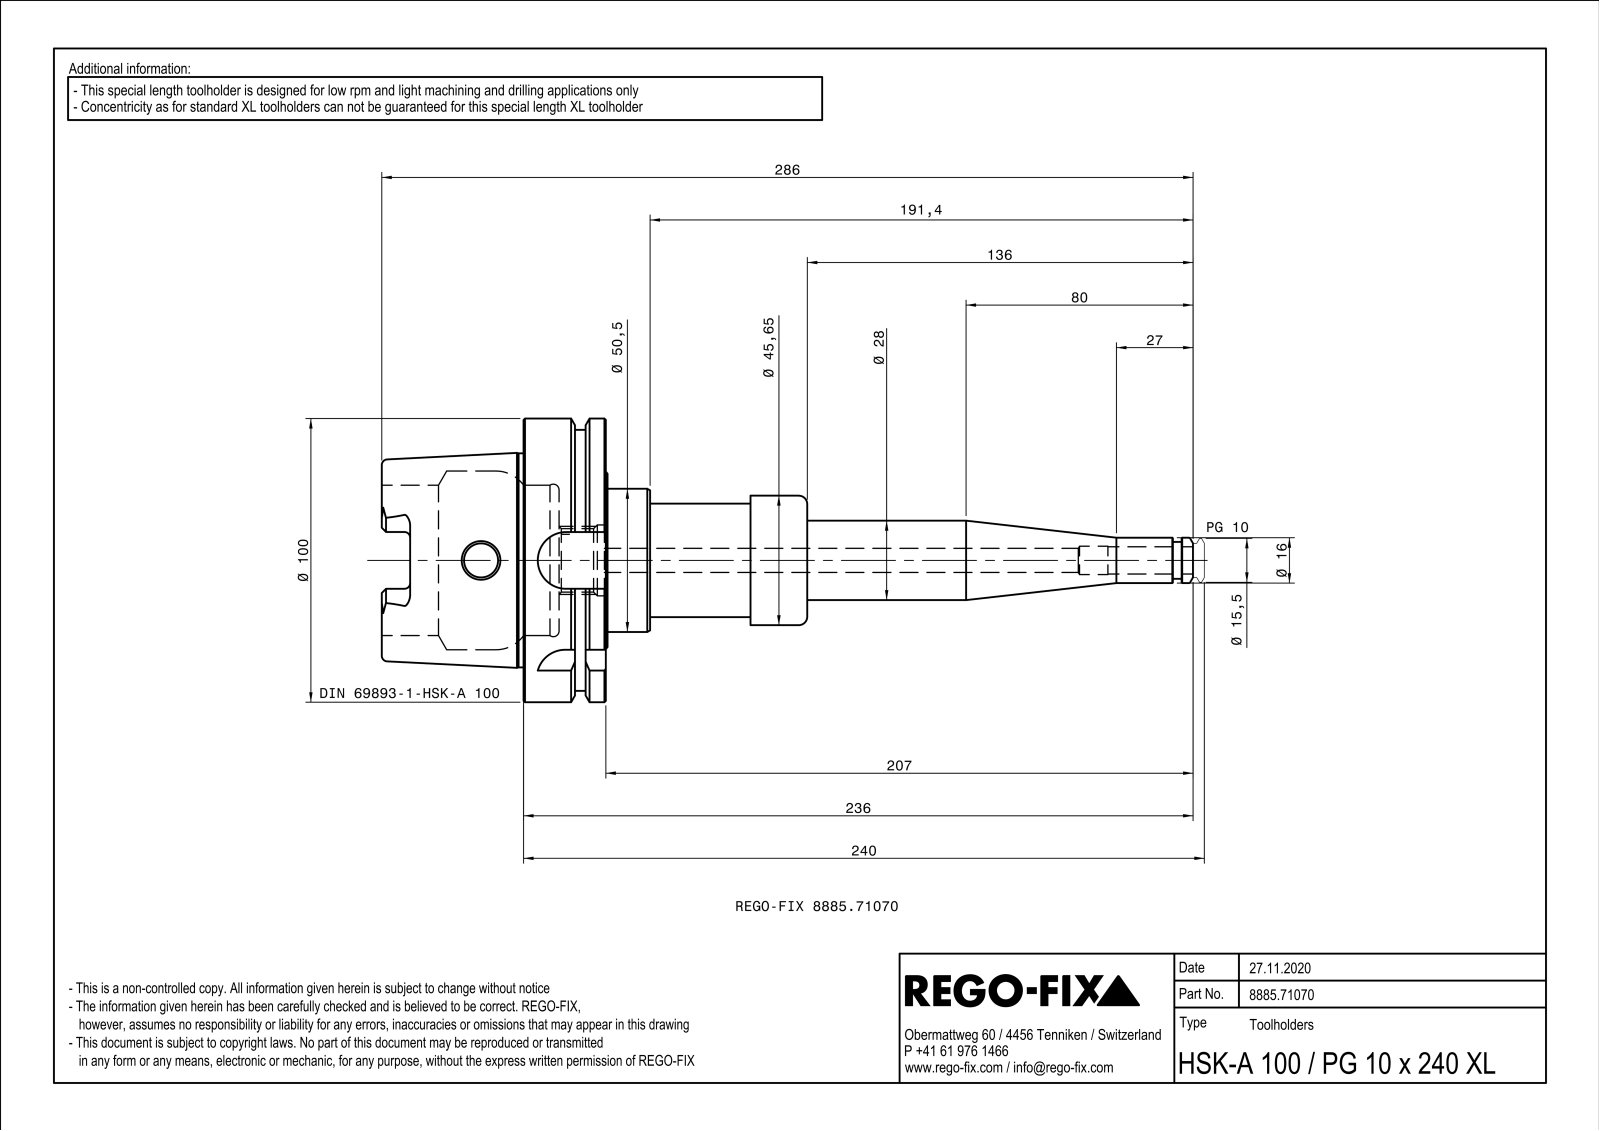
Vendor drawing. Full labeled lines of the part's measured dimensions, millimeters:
Part name (STEP PRODUCT): NOCUT
STEP written by: SIEMENS PLM Software Solid Edge ST10 (AUTOMOTIVE_DESIGN)
Units: millimetres
Bodies: 1 solid, 193 faces (53 planar, 51 cylindrical, 89 other)
Overall size (bounding box): 286 × 100 × 100
Volume: 399 444 mm³ · Surface area: 82 893 mm²
Round holes (diameter × count): ⌀10 ×2, ⌀12 ×2, ⌀8.5 ×1, ⌀9 ×1, ⌀22.38 ×1, ⌀25 ×1, ⌀29 ×1, ⌀38.38 ×1, ⌀40.05 ×1, ⌀43.3 ×1, ⌀53 ×1, ⌀63 ×1
Round bosses / shafts (diameter × count): ⌀100 ×1, ⌀92 ×1, ⌀75.46 ×1, ⌀50.5 ×1, ⌀45.65 ×1, ⌀40 ×1, ⌀34 ×1, ⌀33 ×1
Partial cylindrical surfaces — rounded edges, fillets, slot ends (radius × count): R2 ×6, R4.88 ×4, R10 ×2, R11 ×1, R22.77 ×1
Main face-to-face distances: 29, 12.5, 16.5, 17.1, 79.6, 79, 62.5, 50, 0.6, 29.6
